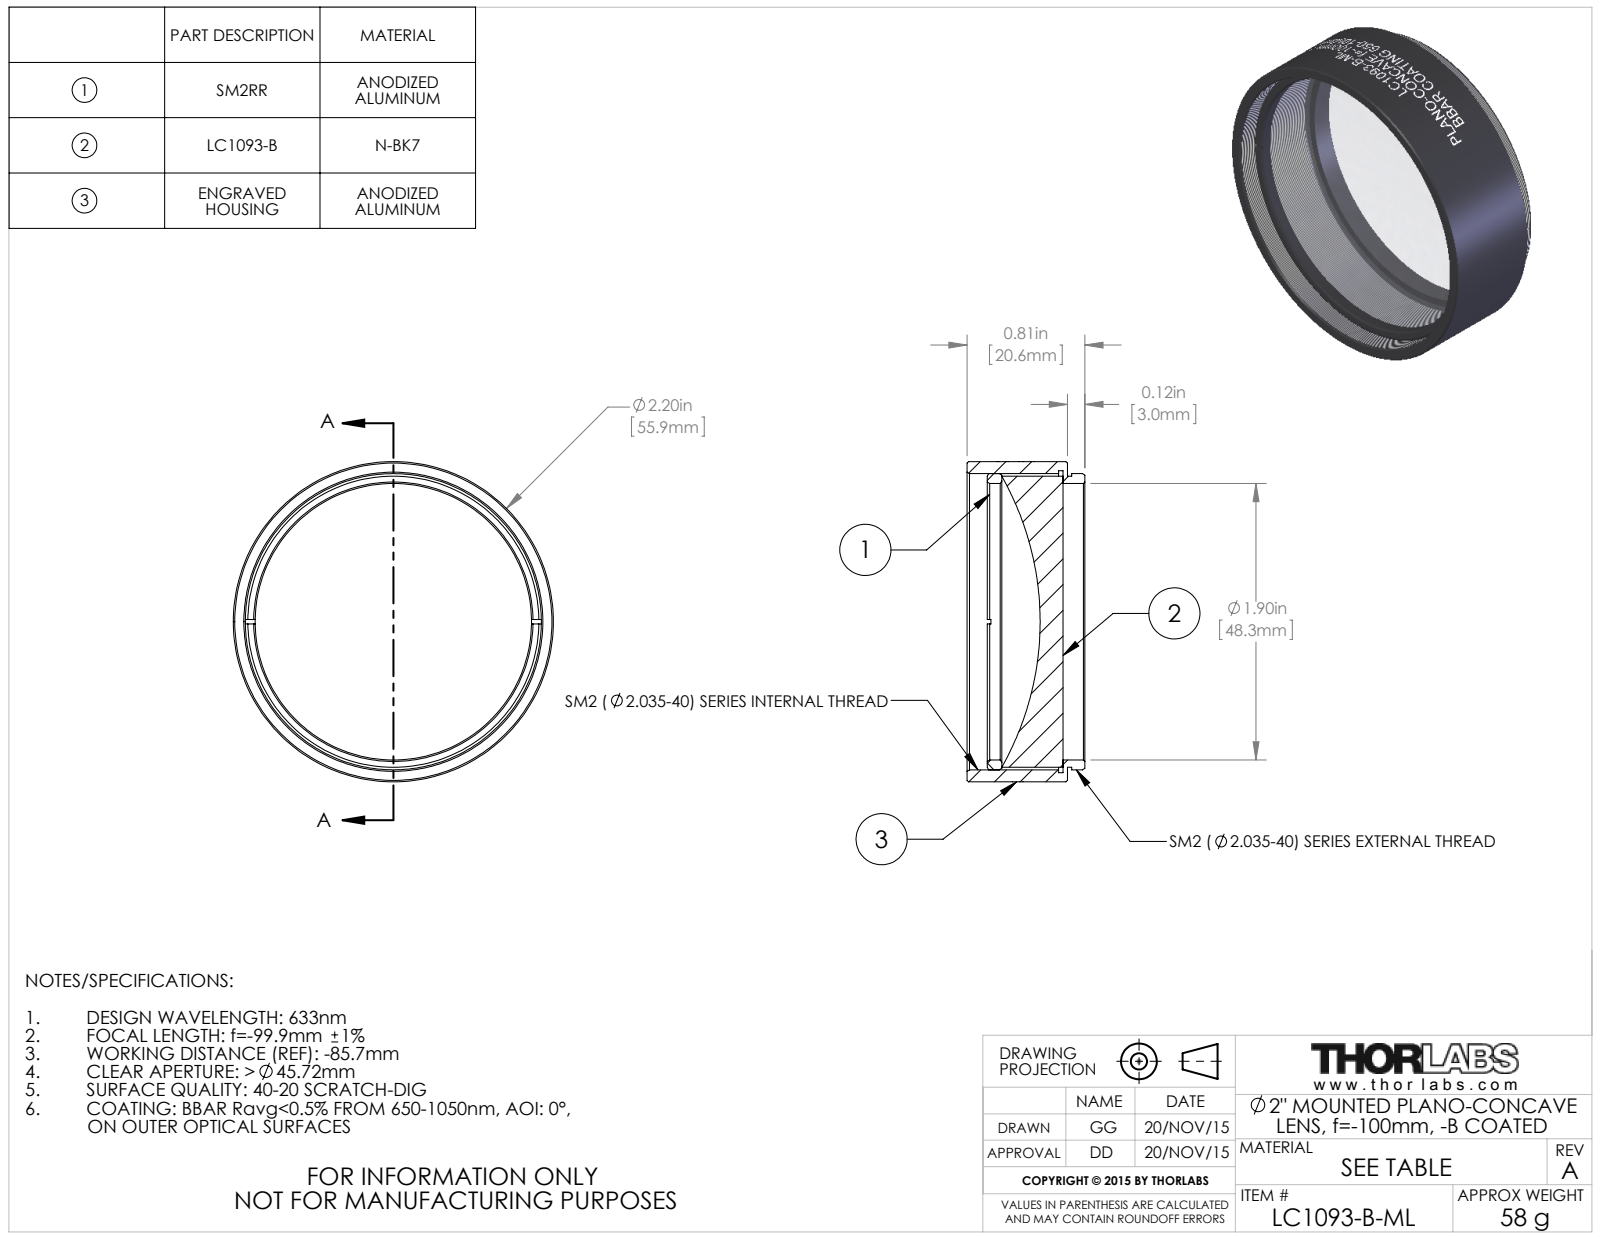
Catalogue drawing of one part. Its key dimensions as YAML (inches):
part_name: "TTN045355-E0W"
step_written_by: "SolidWorks 2014 (CONFIG_CONTROL_DESIGN)"
units: inches
bodies: {solids: 3, faces: 150, planar: 16, cylindrical: 112, other: 22}
overall_size: [2.2, 2.2, 0.81]
volume: 1.371
surface_area: 23.9
round_holes:
  - {diameter: 1.9, count: 1}
  - {diameter: 2.075, count: 1}
round_bosses_or_shafts:
  - {diameter: 2.2, count: 1}
  - {diameter: 2.035, count: 1}
  - {diameter: 2, count: 1}
  - {diameter: 1.999, count: 1}
face_to_face_distances: [0.03, 0.69, 0.66, 0.12, 0.15, 0.81, 0.572, 0.452, 0.422, 0.239]
